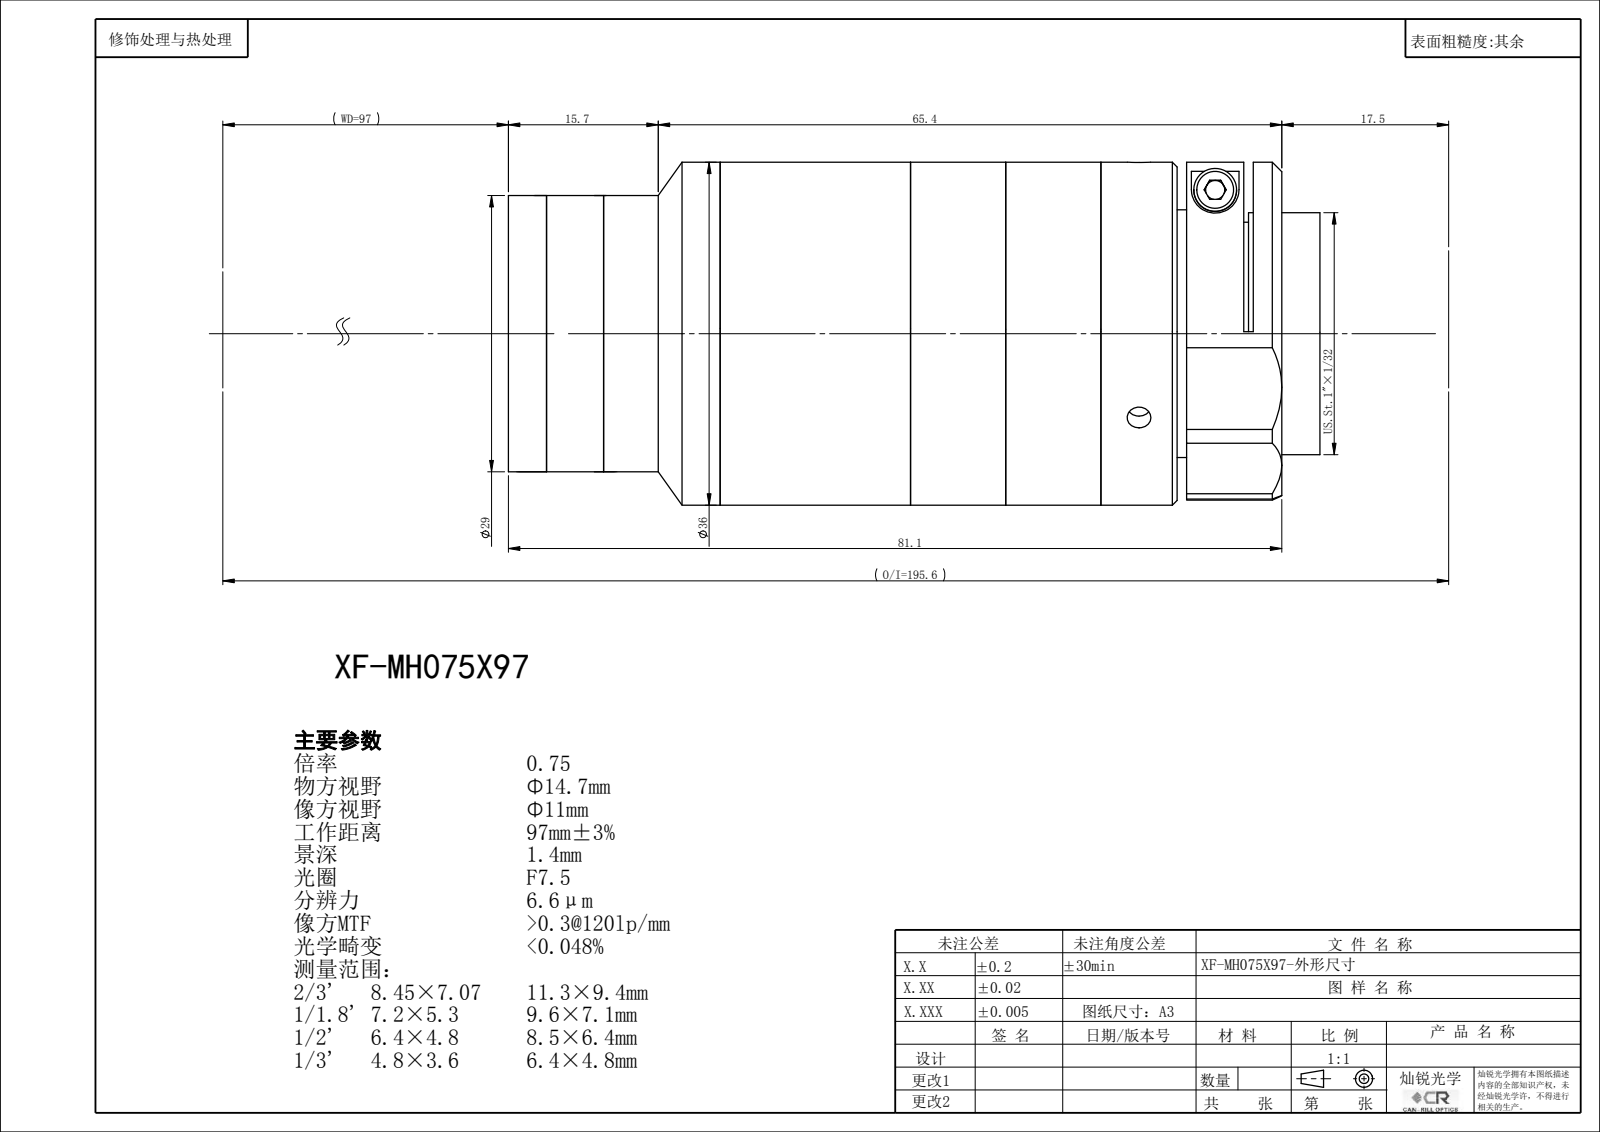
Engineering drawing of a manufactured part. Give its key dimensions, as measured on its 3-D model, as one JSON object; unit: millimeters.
{"part_name": "XF-MH075X97", "step_written_by": "SolidWorks 2022 (CONFIG_CONTROL_DESIGN)", "units": "millimeters", "bodies": {"solids": 0, "faces": 134, "planar": 68, "cylindrical": 44, "other": 22}, "overall_size": [85.13, 36.01, 36], "round_holes": [[2.5, 3], [14, 1], [22.4, 1], [24, 1], [24.9, 1], [26, 1], [26.4, 1]], "round_bosses_or_shafts": [[36, 1], [34, 1], [29, 1], [25.4, 1]], "face_to_face_distances": [10, 20, 18.89, 58.44, 77.33, 1.5, 75.83, 17.39, 38.44, 37.39]}
